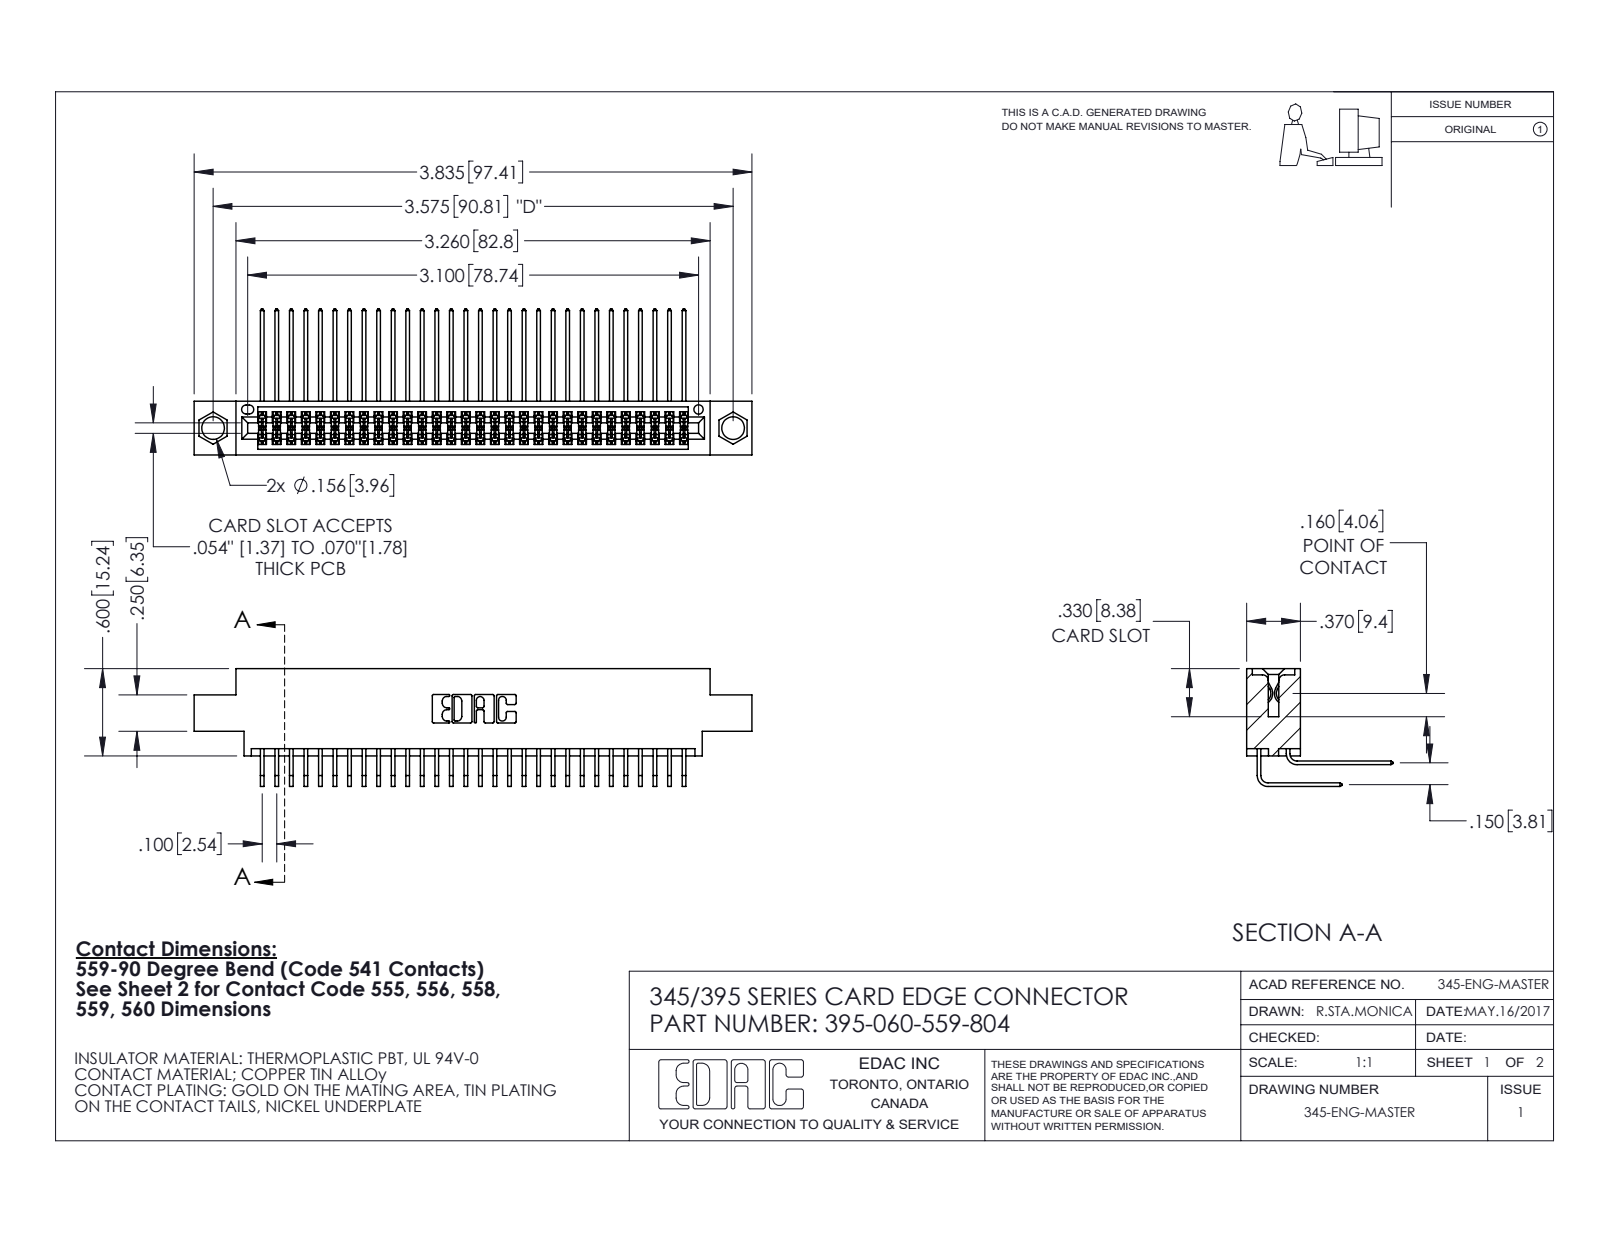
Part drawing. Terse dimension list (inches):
name: 345-292-001_559 Tail - 2; 345-292-001_558 559 Tail - 1; 395-060-559-804; 345 Part_0.170 Offset - 0.156 Dia-TI
written by: SolidWorks 2020 (CONFIG_CONTROL_DESIGN)
unit: in
bodies: 61 solids, 3264 faces (2198 planar, 1066 cylindrical, 0 other)
size: 3.835 × 1.005 × 0.809
volume: 0.578 in³; area: 23.87 in²
holes: 2× ⌀0.156, 1× ⌀0.064
rounds: 119× R0.006, 22× R0.01, 6× R0.007, 6× R0.031, 3× R0.026, 2× R0.014, 2× R0.019, 2× R0.022
face distances: 0.072, 0.298, 0.37, 0.2, 0.098, 0.272, 0.025, 0.225, 0.175, 0.15
hole spacings: 0.27, 3.34, 3.575
